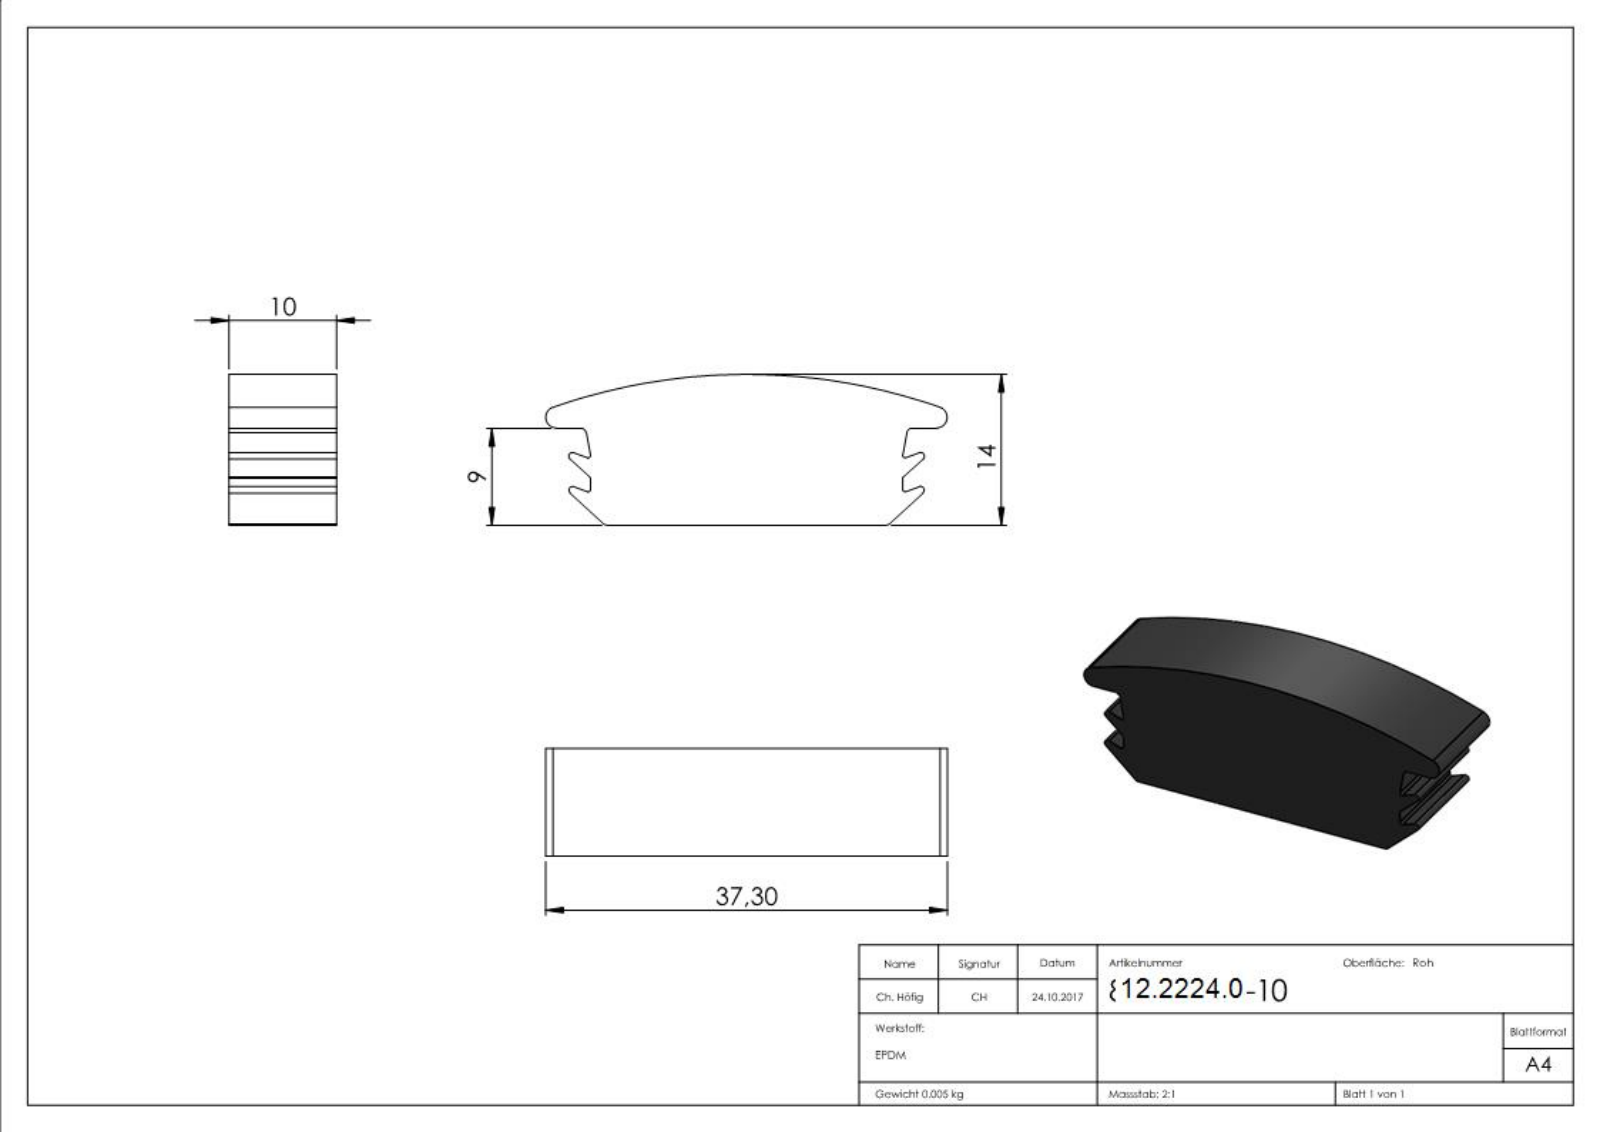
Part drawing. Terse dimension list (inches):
name: 80521-GU-10
written by: SolidWorks 2015 (CONFIG_CONTROL_DESIGN)
unit: in
bodies: 1 solid, 108 faces (17 planar, 49 cylindrical, 42 other)
size: 1.469 × 0.551 × 0.394
volume: 0.253 in³; area: 2.912 in²
rounds: 28× R0.004, 6× R0.008, 4× R0.014, 4× R0.02, 2× R0.039, 1× R2.143
face distances: 0.394, 0.354, 1.142
